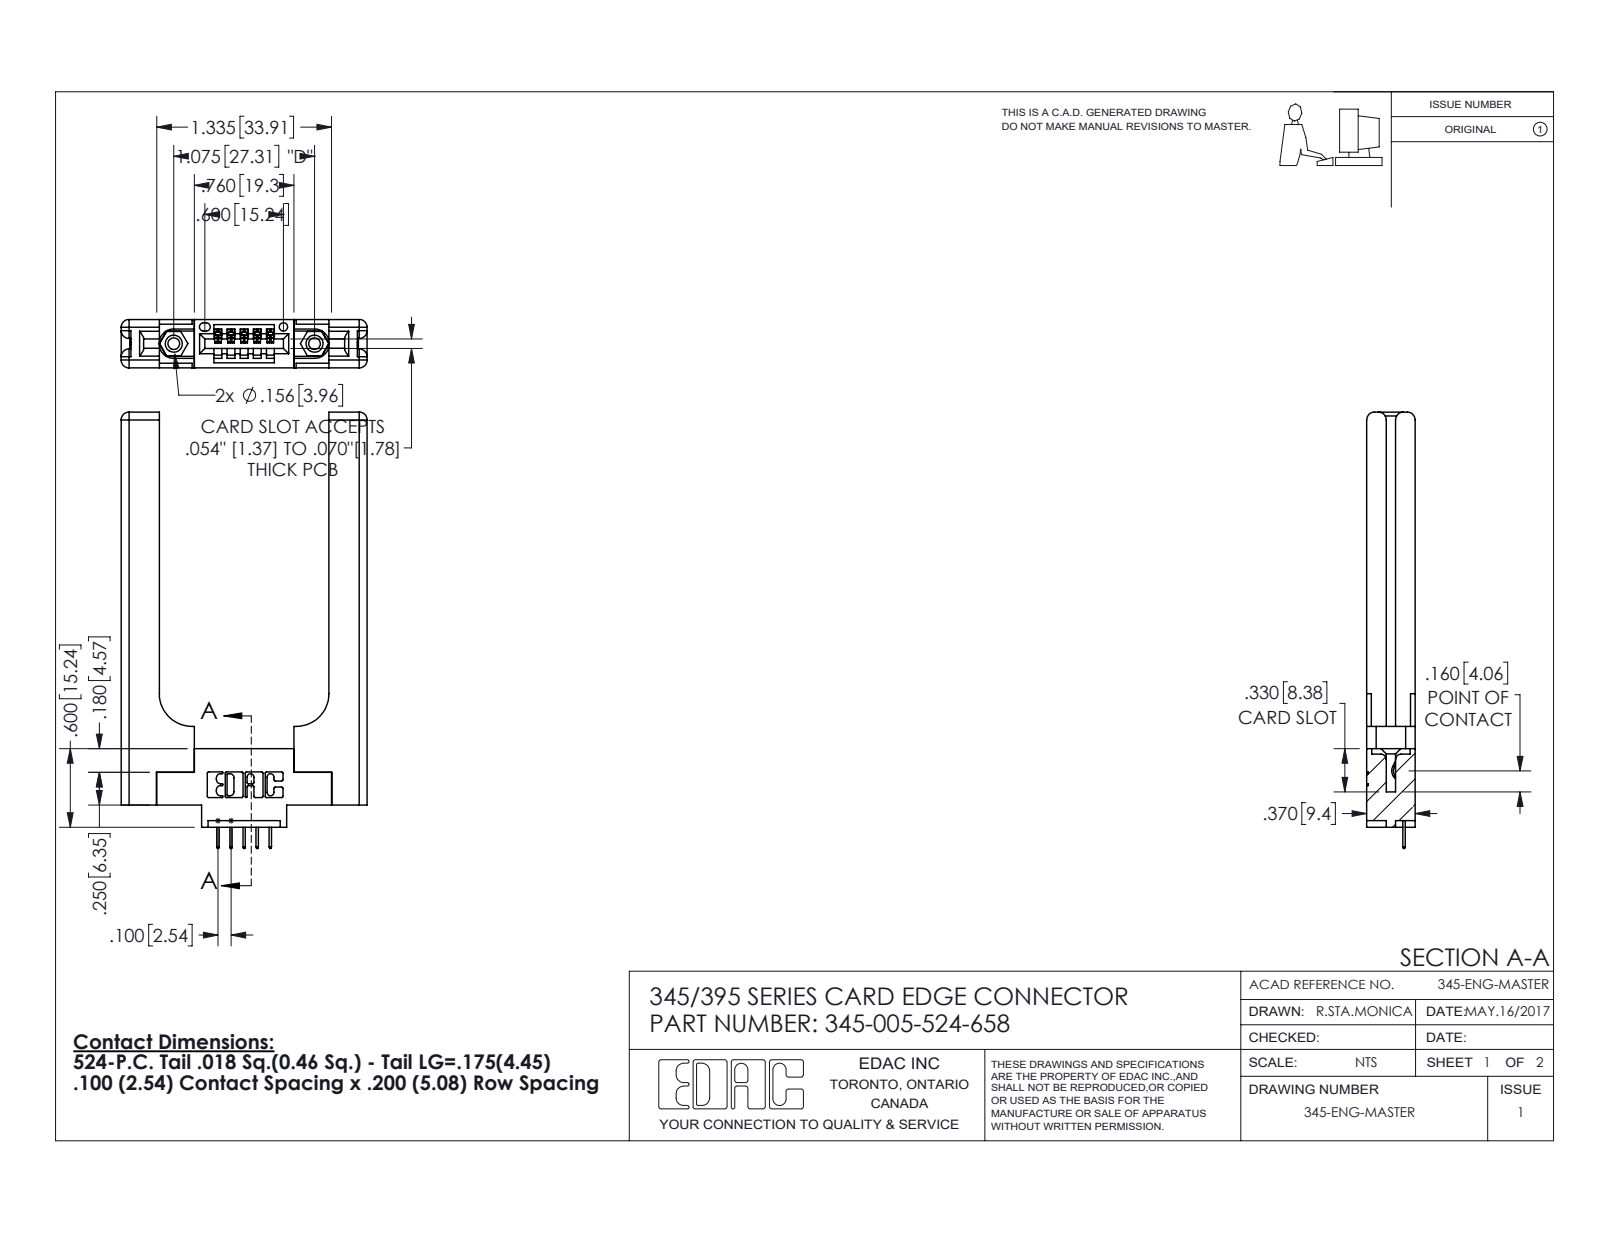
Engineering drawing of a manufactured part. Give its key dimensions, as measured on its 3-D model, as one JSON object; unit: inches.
{"part_name": "345-292-001_345-293-124; 345-005-524-658; 345-220-058_345-220-058; 345-250-001_345-250-001-102 (+1 more)", "step_written_by": "SolidWorks 2016 (CONFIG_CONTROL_DESIGN)", "units": "inches", "bodies": {"solids": 10, "faces": 696, "planar": 462, "cylindrical": 174, "other": 60}, "overall_size": [3.332, 1.879, 0.37], "volume_in3": 0.769, "surface_area_in2": 15.98, "round_holes": [[0.089, 2], [0.125, 2], [0.156, 2], [0.064, 1]], "round_bosses_or_shafts": [[0.155, 2]], "partial_cylinders_radius": [[0.01, 22], [0.06, 16], [0.006, 10], [0.007, 6], [0.031, 6], [0.026, 3], [0.03, 2], [0.031, 2]], "face_to_face_distances": [0.37, 0.15, 0.22, 1.296, 0.072, 0.071, 0.077, 0.148, 0.292, 1.587], "hole_center_spacings": [0.27, 0.847, 1.075]}
